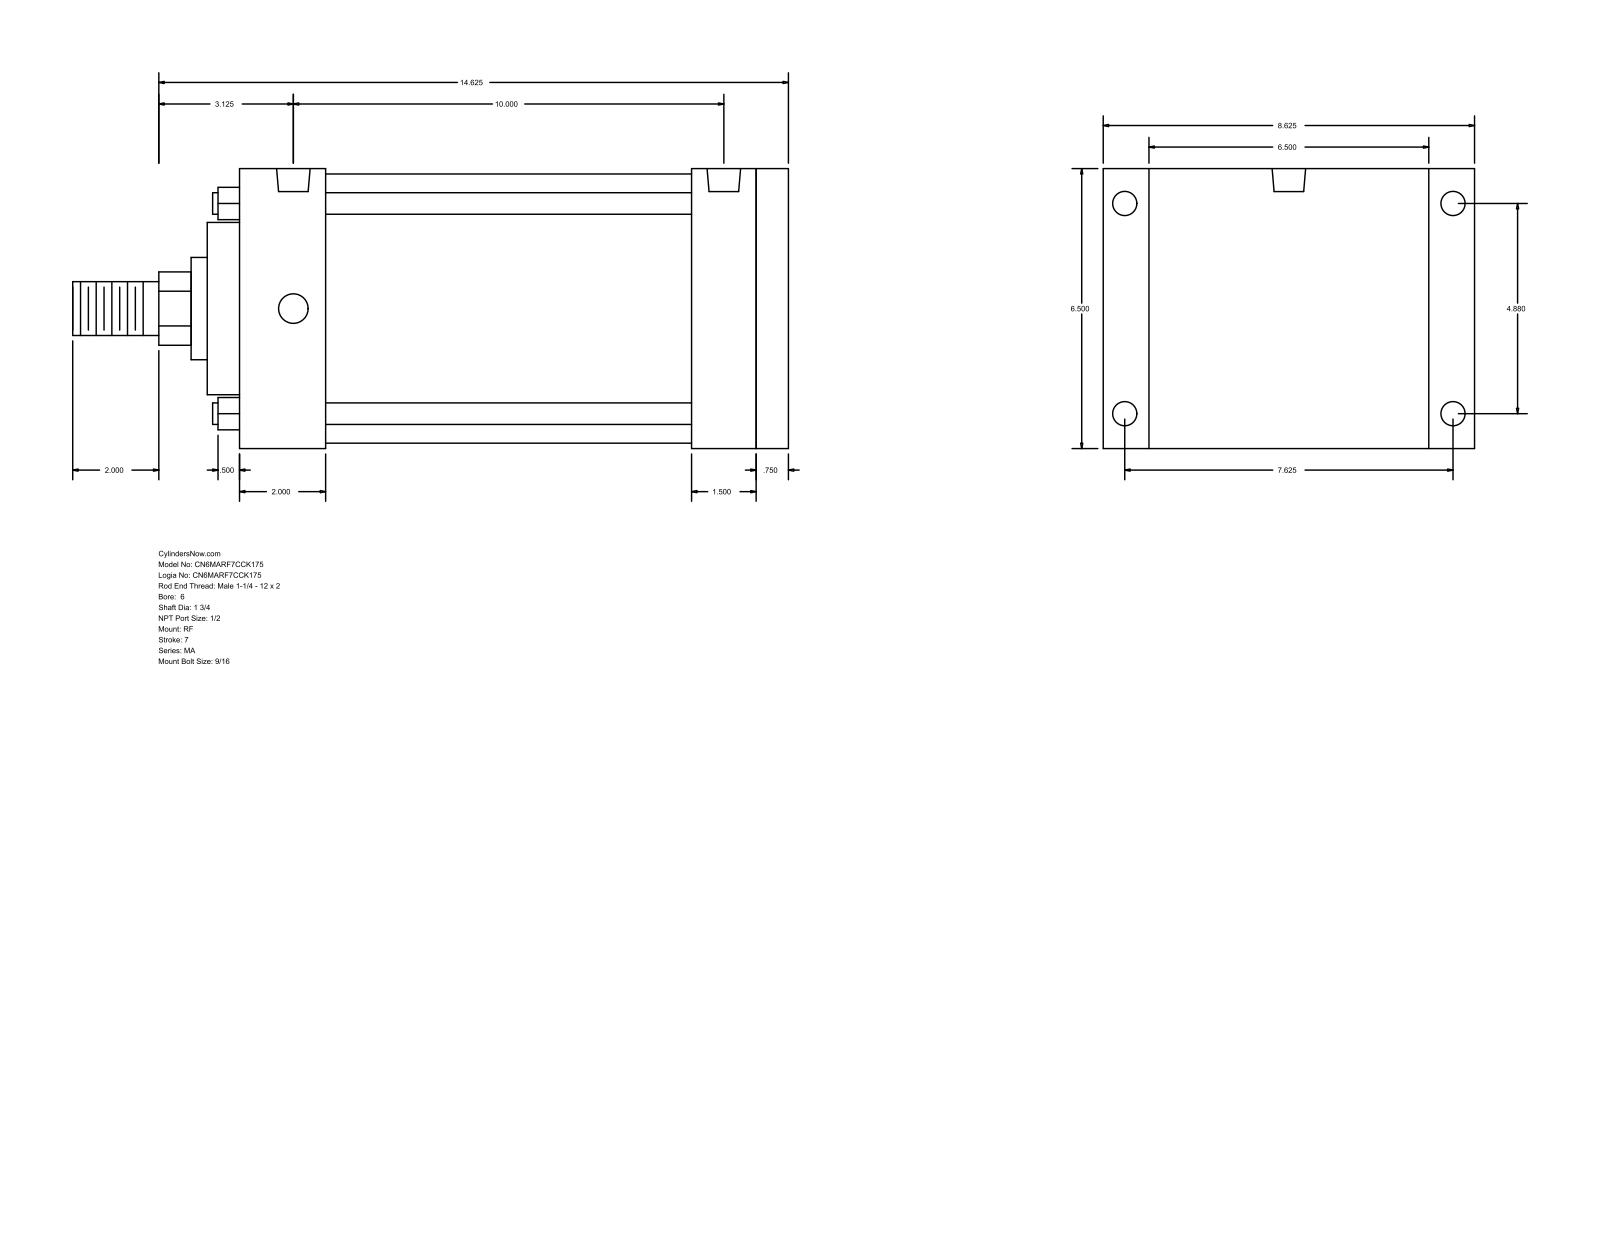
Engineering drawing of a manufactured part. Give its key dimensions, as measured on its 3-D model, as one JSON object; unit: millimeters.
{"part_name": "MA_RF__0600_1.75", "step_written_by": "GSSL Pune (CONFIG_CONTROL_DESIGN)", "units": "millimeters", "bodies": {"solids": 0, "faces": 94, "planar": 65, "cylindrical": 29, "other": 0}, "overall_size": [422.27, 219.07, 165.1], "round_holes": [[14.29, 4], [17.46, 4], [19.77, 2]], "round_bosses_or_shafts": [[12.7, 4], [158.75, 1], [101.6, 1], [60.33, 1], [44.45, 1], [31.75, 1]], "partial_cylinders_radius": [[21.63, 1]], "face_to_face_distances": [165.1, 323.86, 19.05, 304.81, 50.8, 254.01, 273.06, 266.7, 215.9, 38.11], "hole_center_spacings": [123.96, 193.68, 229.95, 254]}
